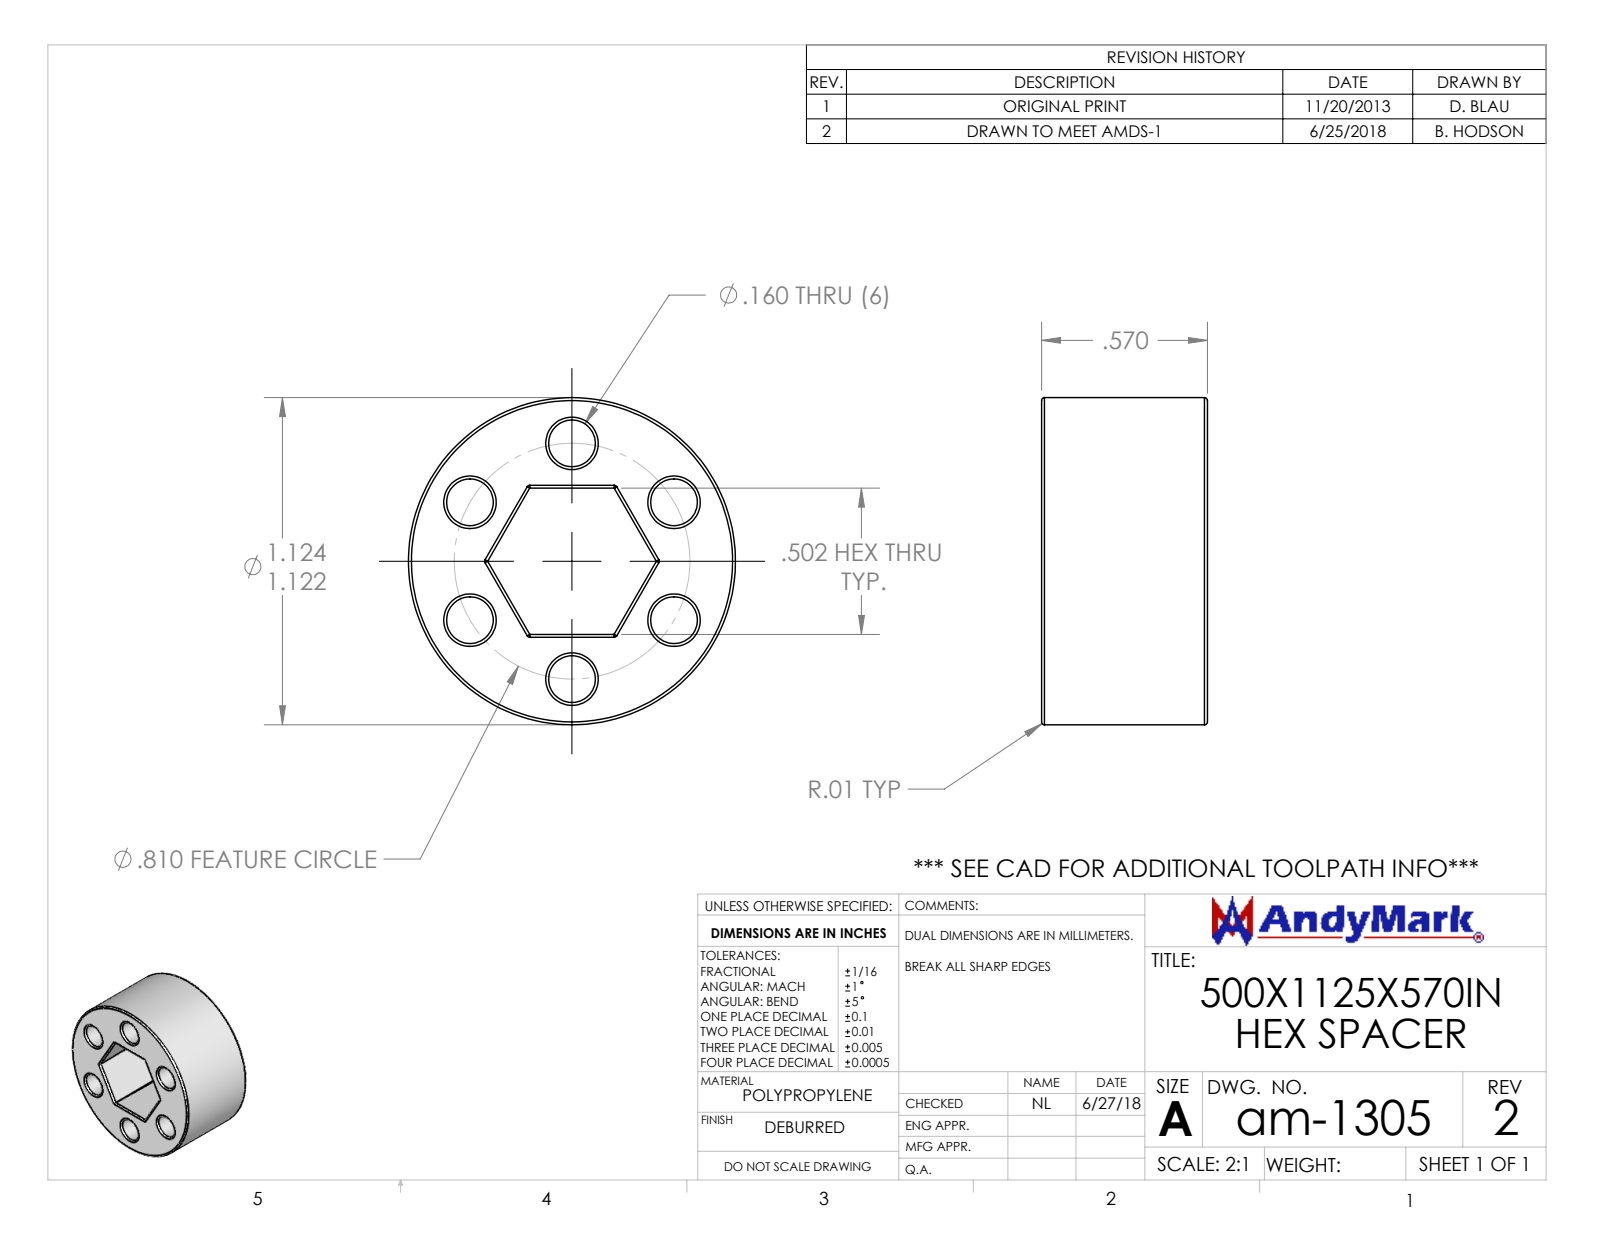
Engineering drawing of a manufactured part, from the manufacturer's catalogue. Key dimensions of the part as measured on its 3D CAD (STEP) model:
Part name (STEP PRODUCT): am-1305 500 Hex Spacer REV2
STEP written by: SolidWorks 2017 (AUTOMOTIVE_DESIGN)
Units: inches
Bodies: 1 solid, 104 faces (8 planar, 20 cylindrical, 76 other)
Overall size (bounding box): 1.124 × 1.124 × 0.57
Volume: 0.358 in³ · Surface area: 6.034 in²
Round bosses / shafts (diameter × count): ⌀1.124 ×1
Partial cylindrical surfaces — rounded edges, fillets, slot ends (radius × count): R0.01 ×12
Main face-to-face distances: 0.57
